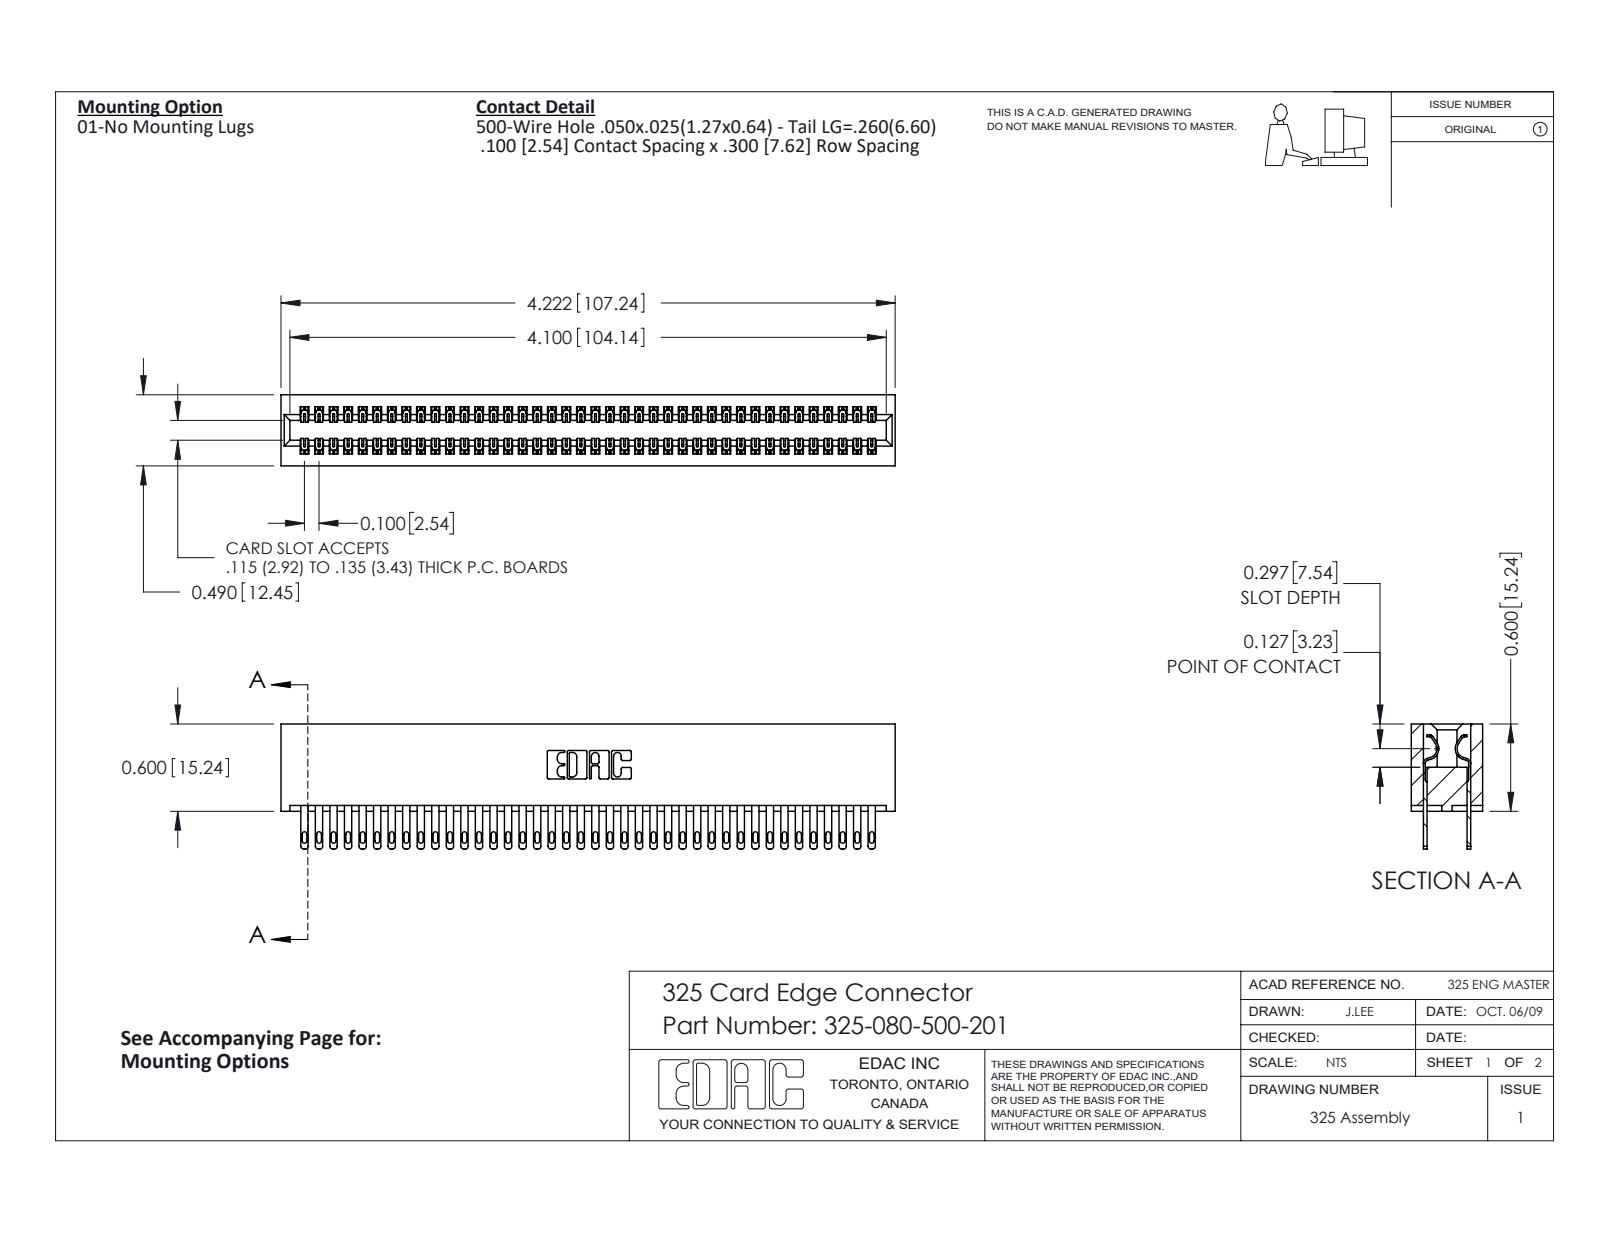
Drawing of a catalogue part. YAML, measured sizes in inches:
part_name: "325-080-500-201; 325 Part_Lugless; 325-292-001_325-293-100"
step_written_by: "SolidWorks 2016 (CONFIG_CONTROL_DESIGN)"
units: inches
bodies: {solids: 81, faces: 3946, planar: 2466, cylindrical: 1480, other: 0}
overall_size: [4.222, 0.86, 0.49]
volume: 0.896
surface_area: 29.78
partial_cylinders:
  - {radius: 0.006, count: 120}
  - {radius: 0.016, count: 80}
  - {radius: 0.02, count: 80}
  - {radius: 0.01, count: 22}
  - {radius: 0.007, count: 6}
  - {radius: 0.031, count: 6}
  - {radius: 0.026, count: 3}
  - {radius: 0.014, count: 2}
face_to_face_distances: [0.083, 0.407, 0.3, 0.107, 0.383, 0.025, 0.325, 0.49, 0.275, 0.56]
